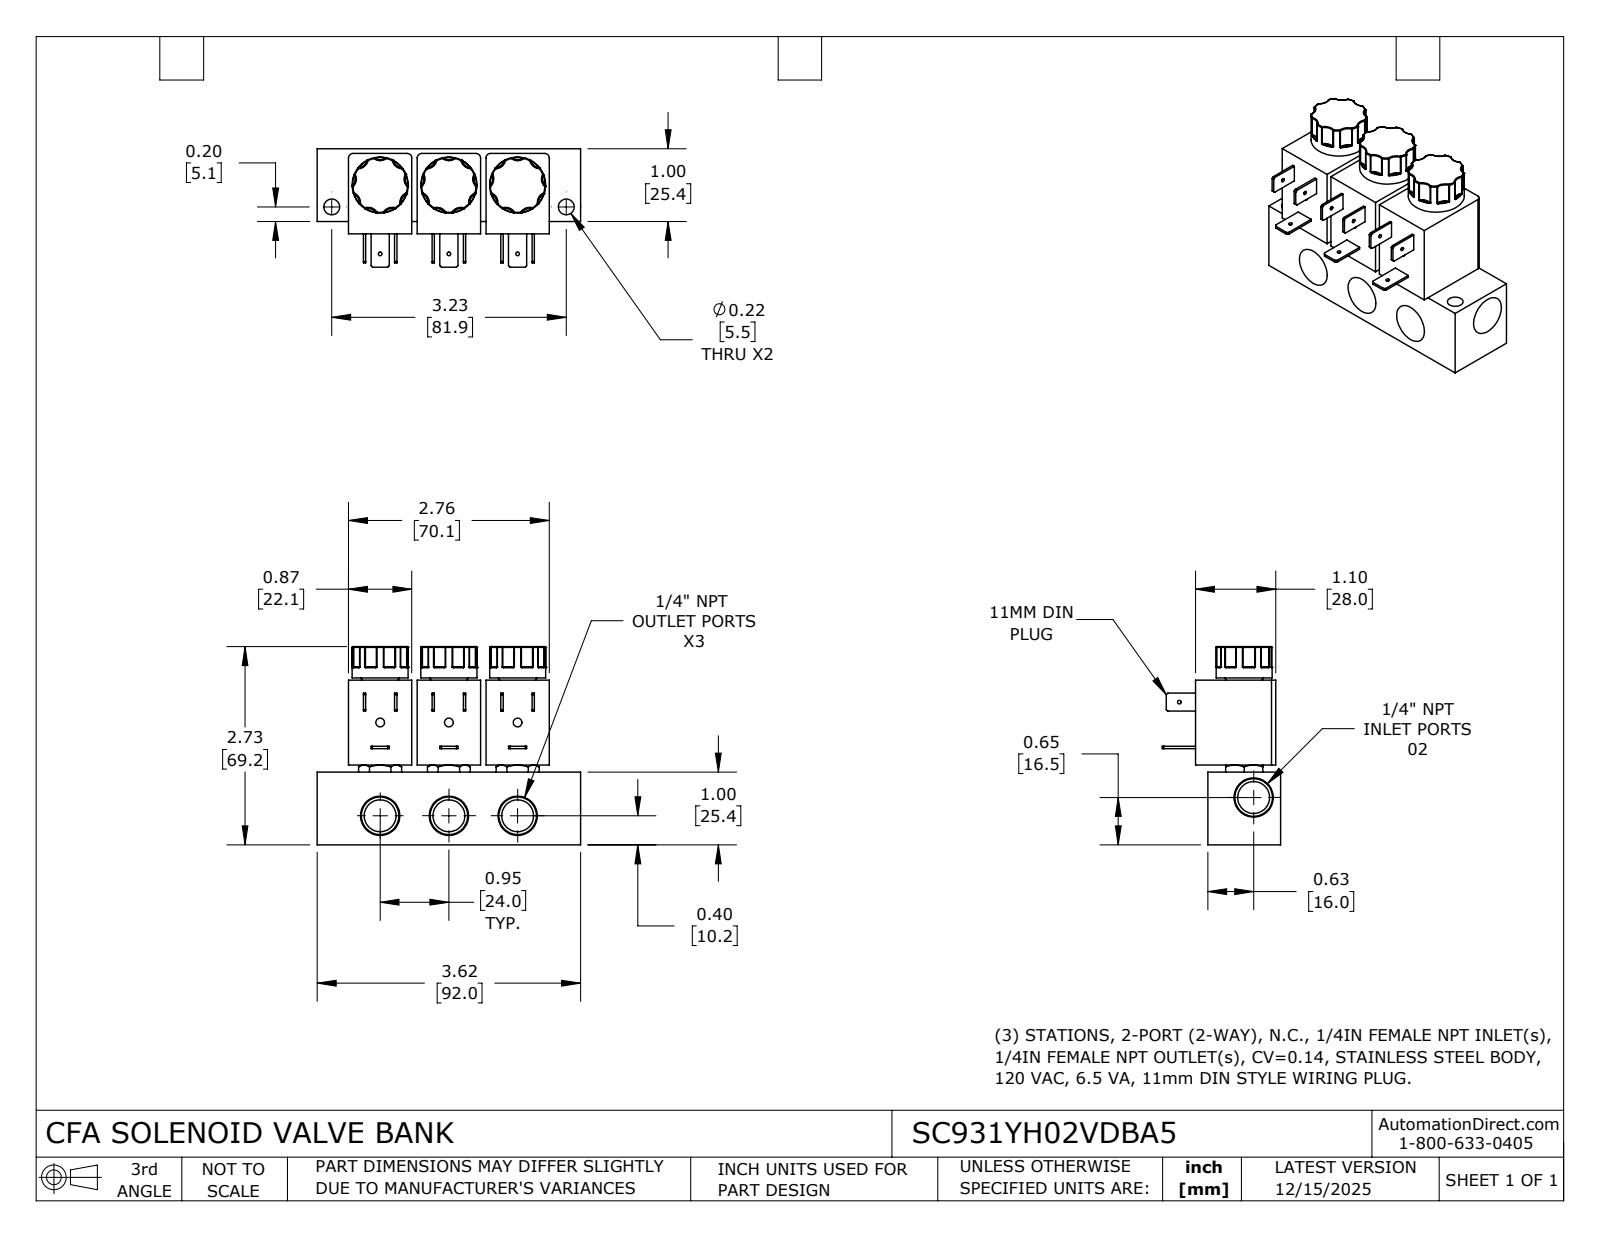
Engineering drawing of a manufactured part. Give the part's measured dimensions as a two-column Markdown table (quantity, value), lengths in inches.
| quantity | value |
| --- | --- |
| part name | SC931YH02VDBA5 |
| STEP written by | SolidWorks 2024 (CONFIG_CONTROL_DESIGN) |
| units | inches |
| bodies | 1 solid, 657 faces (146 planar, 140 cylindrical, 371 other) |
| overall size | 3.622 × 2.725 × 1.627 |
| volume | 7.008 in³ |
| surface area | 47.81 in² |
| round holes (diameter × count) | 0.05 × 4, 0.438 × 4, 0.12 × 3, 0.217 × 2 |
| round bosses / shafts (diameter × count) | 0.77 × 3 |
| partial cylindrical surfaces (radius × count) | 0.01 × 54, 0.133 × 25, 0.06 × 6, 0.132 × 2 |
| main face-to-face distances | 1, 0.945, 0.87, 1.169, 0.169, 0.065, 0.935, 1.104, 1.89, 1.815 |
| hole center spacings | 0.945, 1.593, 1.282, 1.89, 2.283, 0.928, 0.93, 1.662 |
